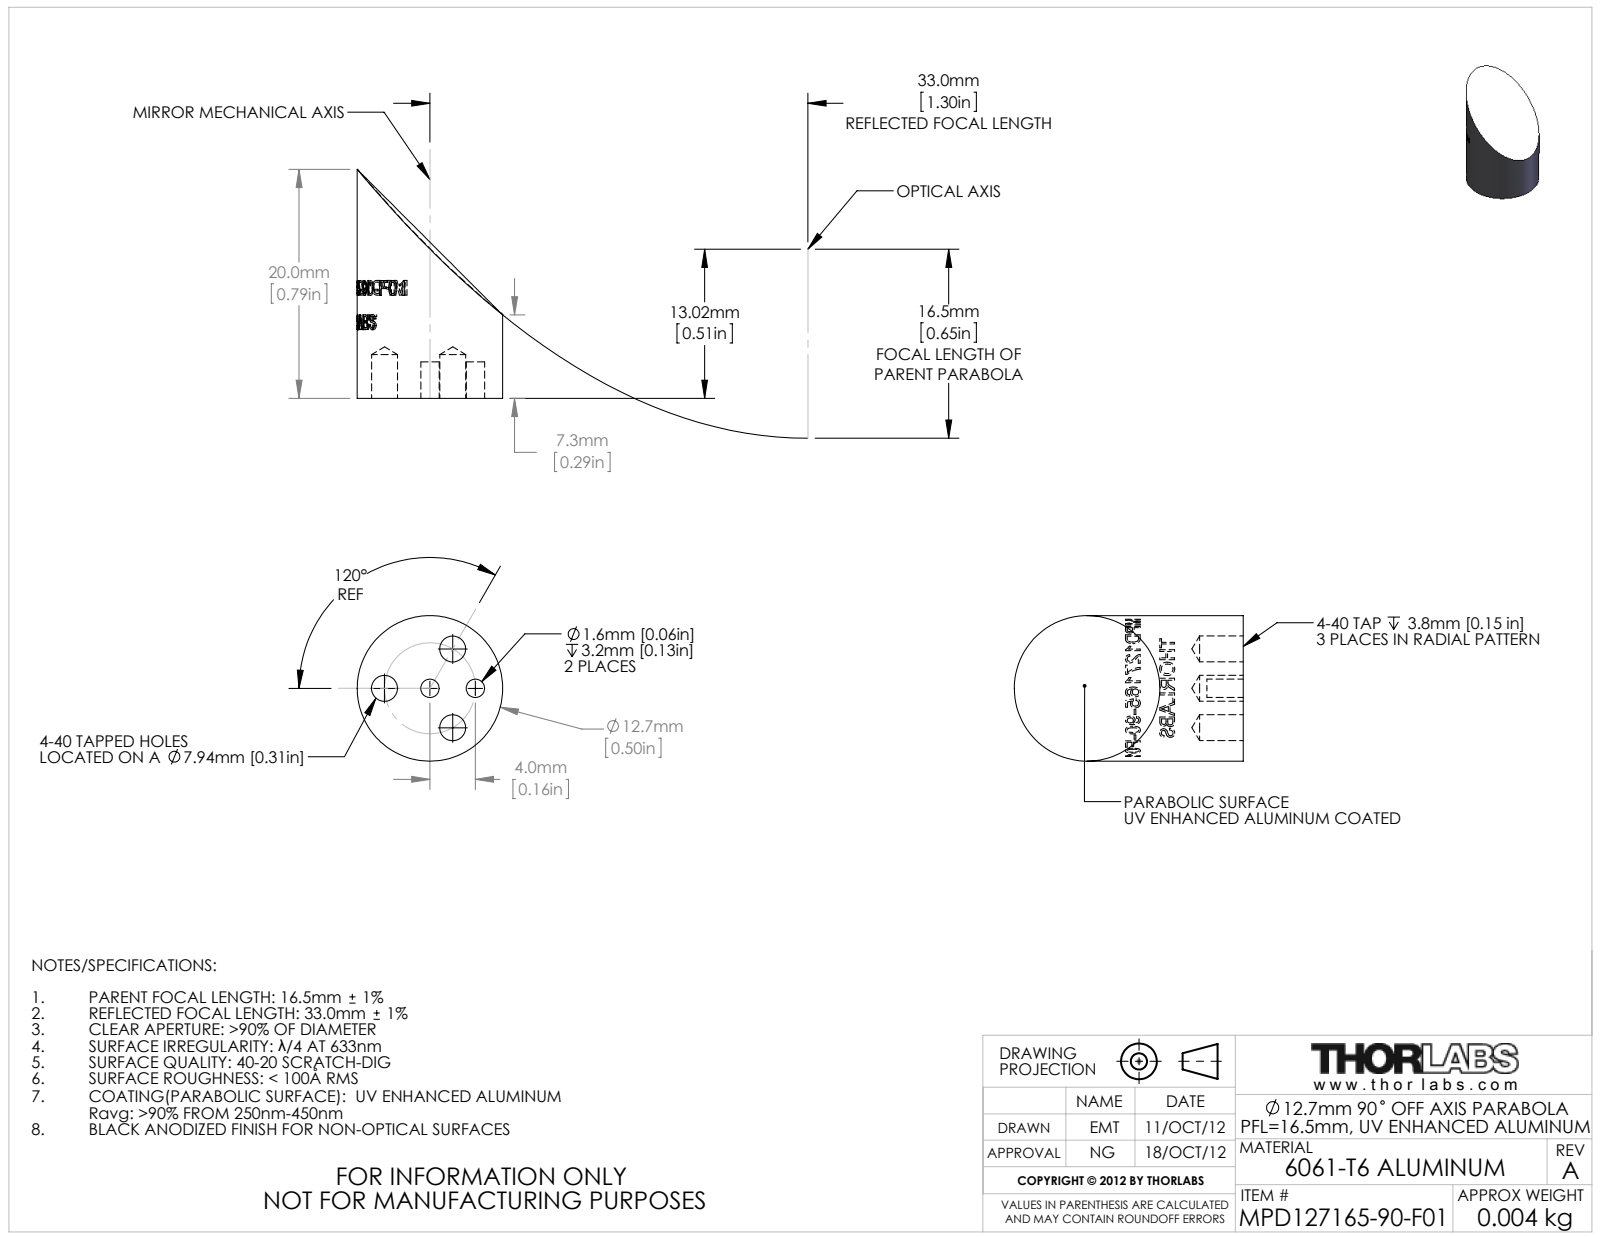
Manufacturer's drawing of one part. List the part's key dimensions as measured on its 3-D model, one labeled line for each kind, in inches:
Part name (STEP PRODUCT): TTN005548-E0W
STEP written by: SolidWorks 2012 (CONFIG_CONTROL_DESIGN)
Units: inches
Bodies: 1 solid, 59 faces (3 planar, 48 cylindrical, 8 other)
Overall size (bounding box): 0.787 × 0.5 × 0.5
Volume: 0.099 in³ · Surface area: 1.496 in²
Round holes (diameter × count): ⌀0.089 ×3, ⌀0.063 ×2
Round bosses / shafts (diameter × count): ⌀0.5 ×1
Main face-to-face distances: 0.125
Hole centre spacings: 0.156, 0.27, 0.271, 0.313
